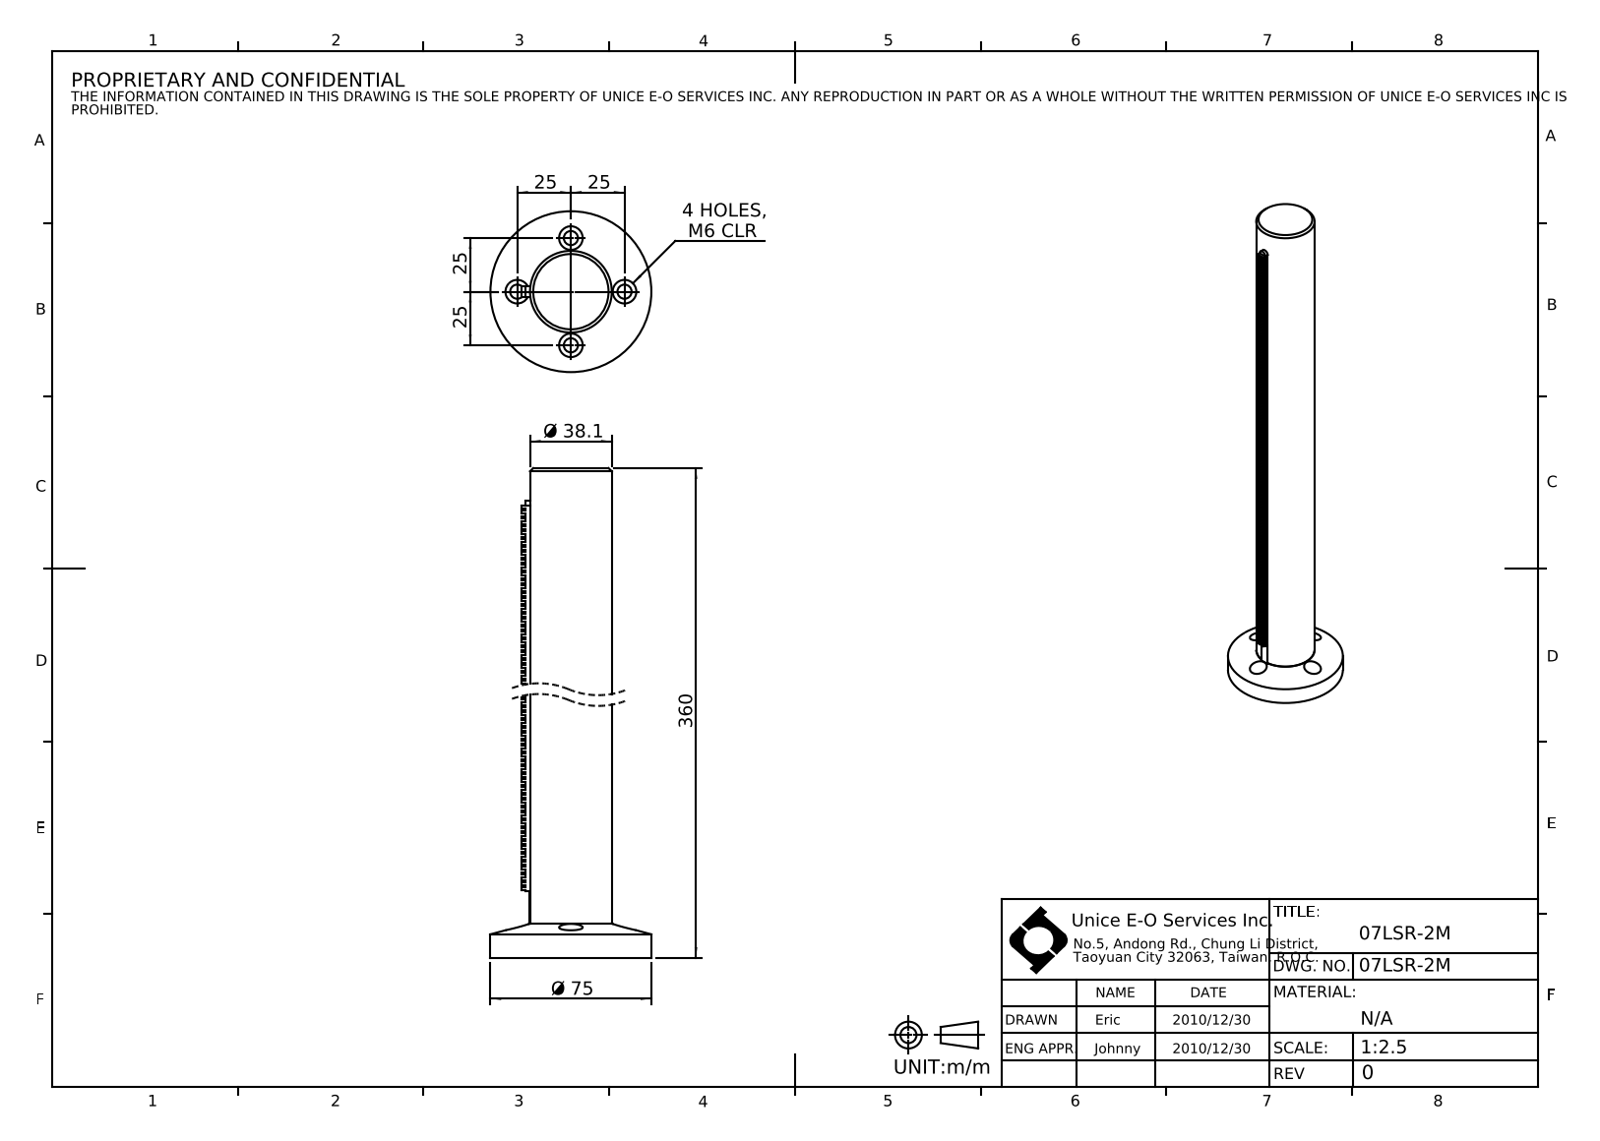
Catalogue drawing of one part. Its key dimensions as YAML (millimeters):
part_name: "07LSR-2M"
step_written_by: "SolidWorks 2016 (CONFIG_CONTROL_DESIGN)"
units: millimeters
bodies: {solids: 3, faces: 595, planar: 551, cylindrical: 38, other: 6}
overall_size: [360, 75, 75]
volume: 451408
surface_area: 74899
round_holes:
  - {diameter: 6.6, count: 5}
  - {diameter: 11, count: 5}
  - {diameter: 5, count: 1}
  - {diameter: 25, count: 1}
round_bosses_or_shafts:
  - {diameter: 75, count: 1}
  - {diameter: 38.1, count: 1}
partial_cylinders:
  - {radius: 2.5, count: 1}
  - {radius: 3.95, count: 1}
  - {radius: 5.25, count: 1}
face_to_face_distances: [1.6, 5, 16, 1.45, 6.45, 1.3, 2.75, 7.75, 9.2, 360]
hole_center_spacings: [25, 35.36, 50]
